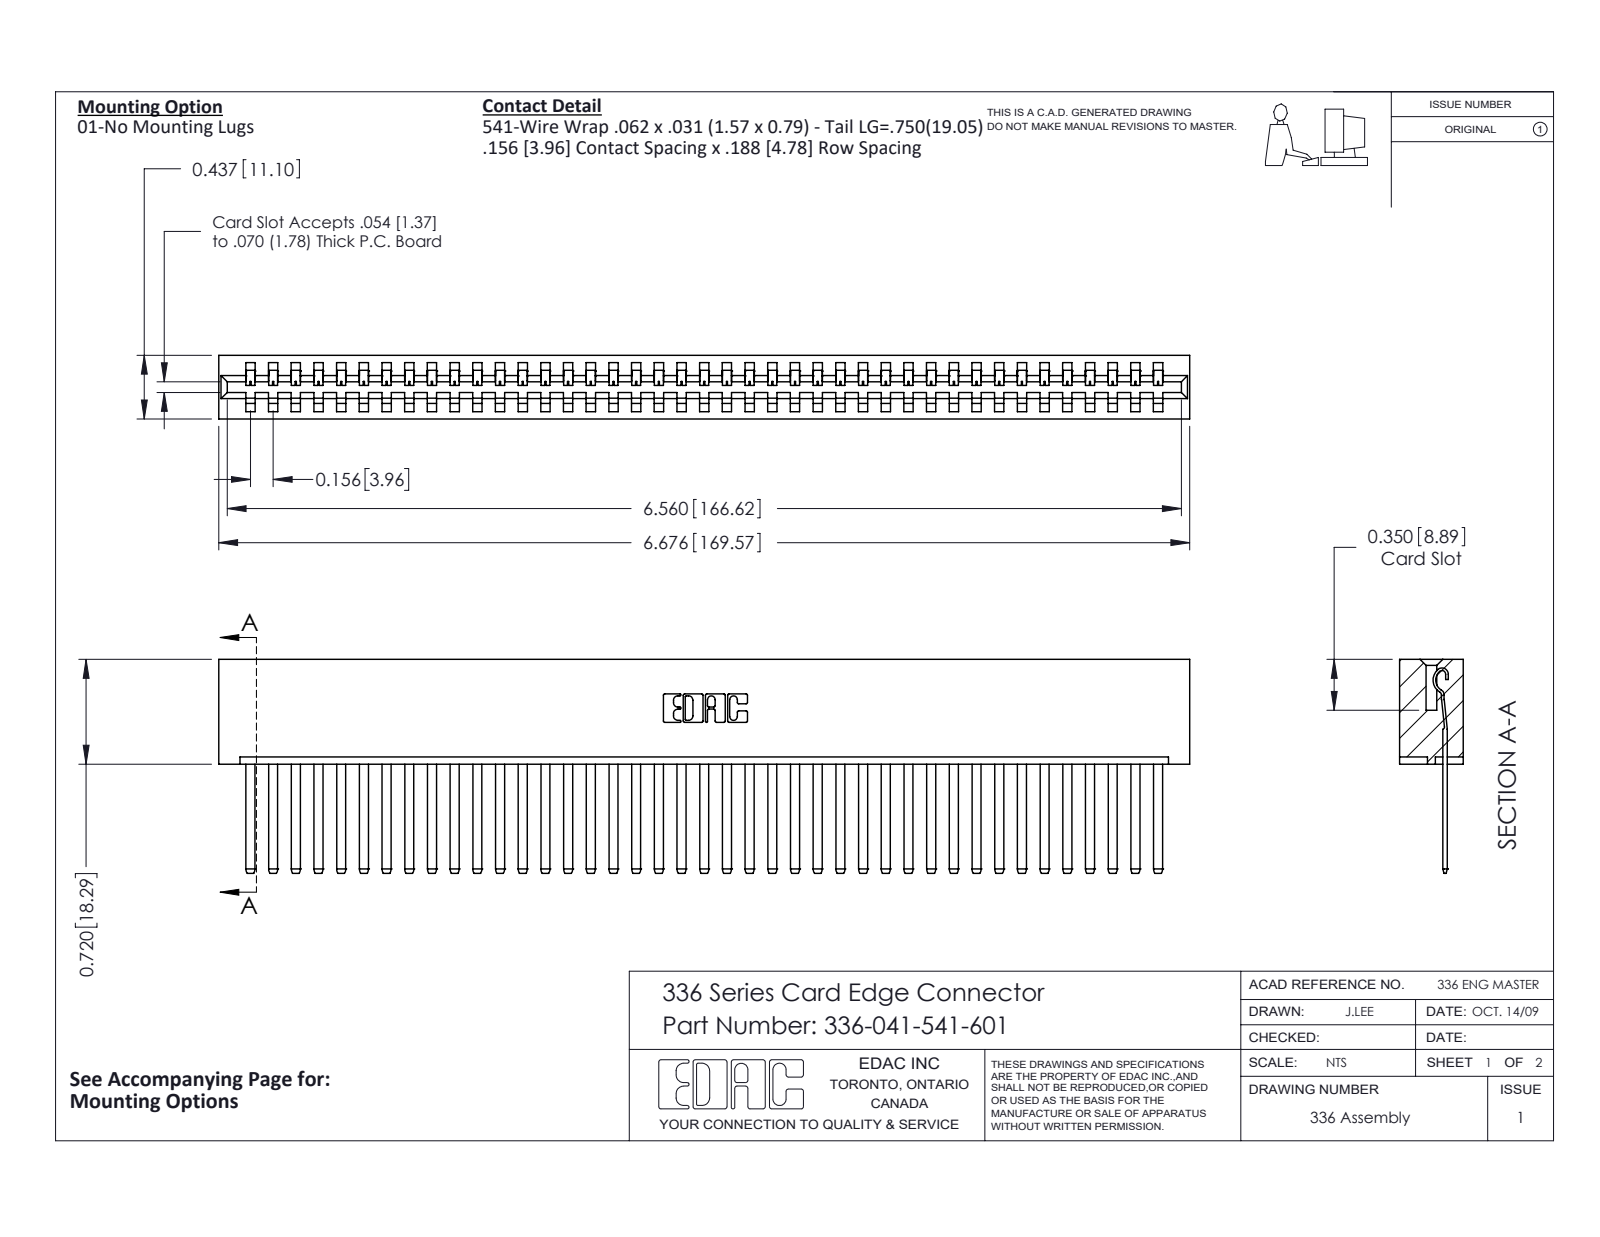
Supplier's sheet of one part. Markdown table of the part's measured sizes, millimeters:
| quantity | value |
| --- | --- |
| part name | 336-290-001_336-290-541; 336-041-541-601; 336 Part_Lugless |
| STEP written by | SolidWorks 2020 (CONFIG_CONTROL_DESIGN) |
| units | millimeters |
| bodies | 42 solids, 2156 faces (1460 planar, 696 cylindrical, 0 other) |
| overall size | 169.6 × 37.3 × 11.1 |
| volume | 26 220 mm³ |
| surface area | 28 550 mm² |
| partial cylindrical surfaces (radius × count) | 0.1 × 82, 1.4 × 82, 0.3 × 22, 0.2 × 6, 0.8 × 6, 0.7 × 3, 0.6 × 2, 1 × 2 |
| main face-to-face distances | 11.1, 4.6, 8.3, 3.6, 7.5, 2.8, 0.8, 6.5, 1.3, 9.8 |
